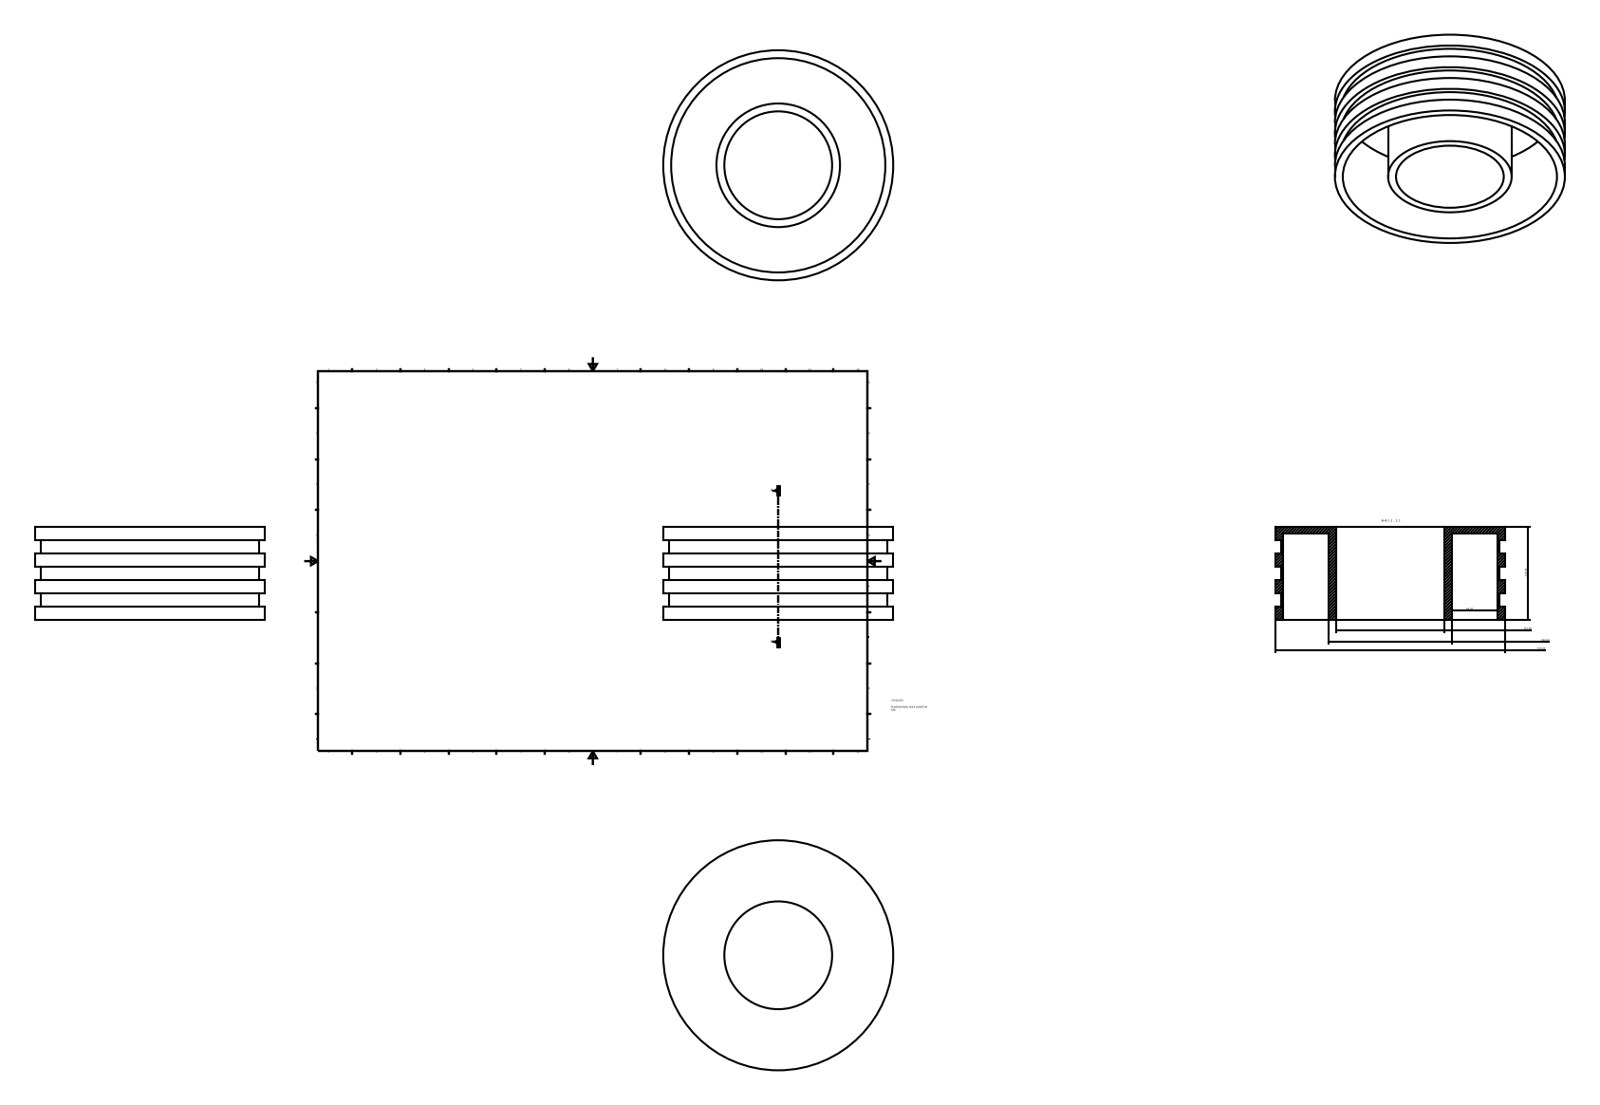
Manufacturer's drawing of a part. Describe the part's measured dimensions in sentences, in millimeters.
The part is named "37020180". Its 3-D file was written by "Autodesk Inventor 2015 (AUTOMOTIVE_DESIGN)". It is 1 solid with 20 faces: 10 planar, 10 cylindrical and 0 other. Overall it measures 335 by 335 by 135 millimeters. Its volume is 2 394 000 cubic millimeters and its surface area 588 507 square millimeters. Round holes: 1 of diameter 157, 1 of diameter 312. Round bosses or shafts: 1 of diameter 335, 1 of diameter 318.25, 1 of diameter 180. The main face-to-face distances are 38.57, 9.64, 77.14, 19.29, 57.86, 19.28, 125.36, 135, 96.43, 115.71.
